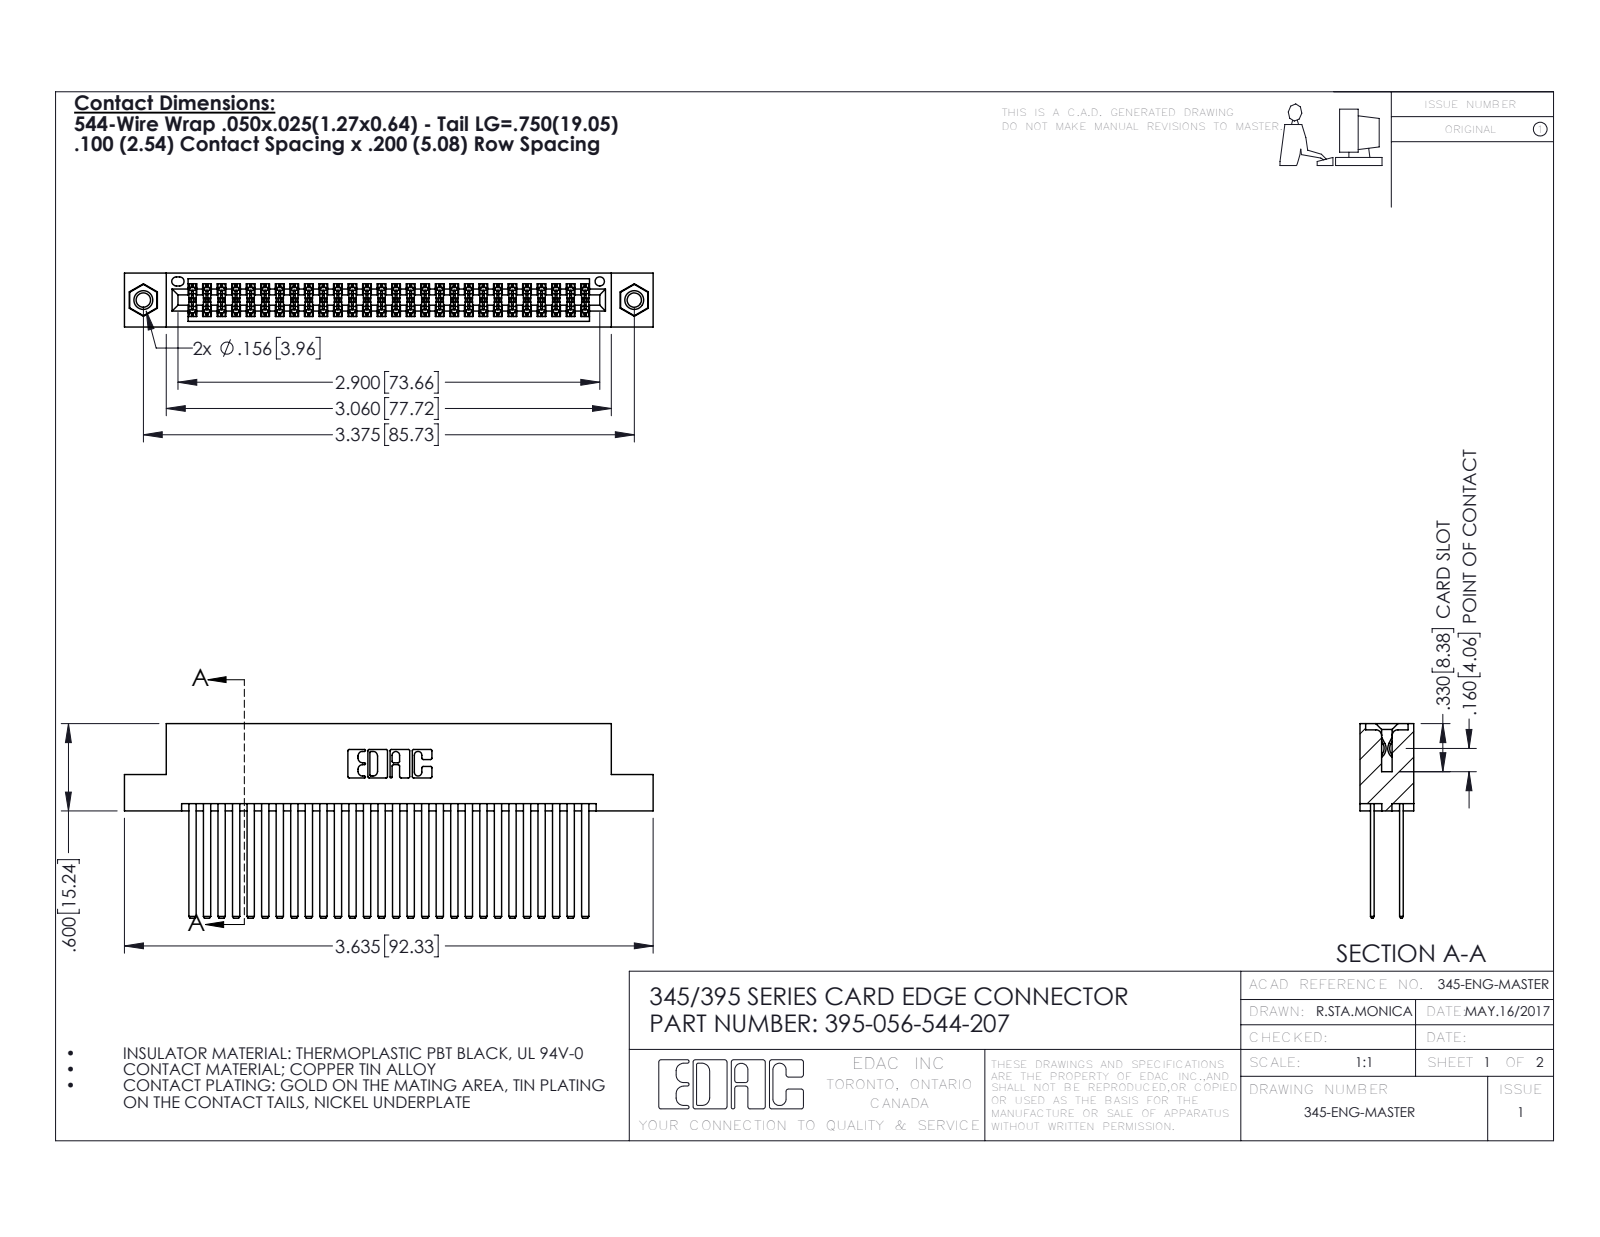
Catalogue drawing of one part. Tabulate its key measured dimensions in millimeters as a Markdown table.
| quantity | value |
| --- | --- |
| part name | 345-250-001_345-250-005-103; 345-292-001_345-293-144; 345 Part_Flush Mounting Lugs - 0.156 Dia-TI; 395-056-544-207 |
| STEP written by | SolidWorks 2016 (CONFIG_CONTROL_DESIGN) |
| units | millimeters |
| bodies | 59 solids, 2650 faces (1736 planar, 898 cylindrical, 16 other) |
| overall size | 92.3 × 34 × 9.4 |
| volume | 9 600 mm³ |
| surface area | 16 260 mm² |
| round holes (diameter × count) | 2.5 × 2, 3.2 × 2, 4 × 2, 1.6 × 1 |
| round bosses / shafts (diameter × count) | 3.9 × 2 |
| partial cylindrical surfaces (radius × count) | 0.2 × 84, 0.3 × 22, 0.2 × 6, 0.8 × 6, 0.7 × 3, 0.4 × 2, 0.5 × 2, 0.6 × 2 |
| main face-to-face distances | 5.1, 0.6, 1.8, 7.6, 2.5, 6.9, 5.7, 4.4, 9.4, 1.3 |
| hole center spacings | 6.9, 79.8, 85.7 |
